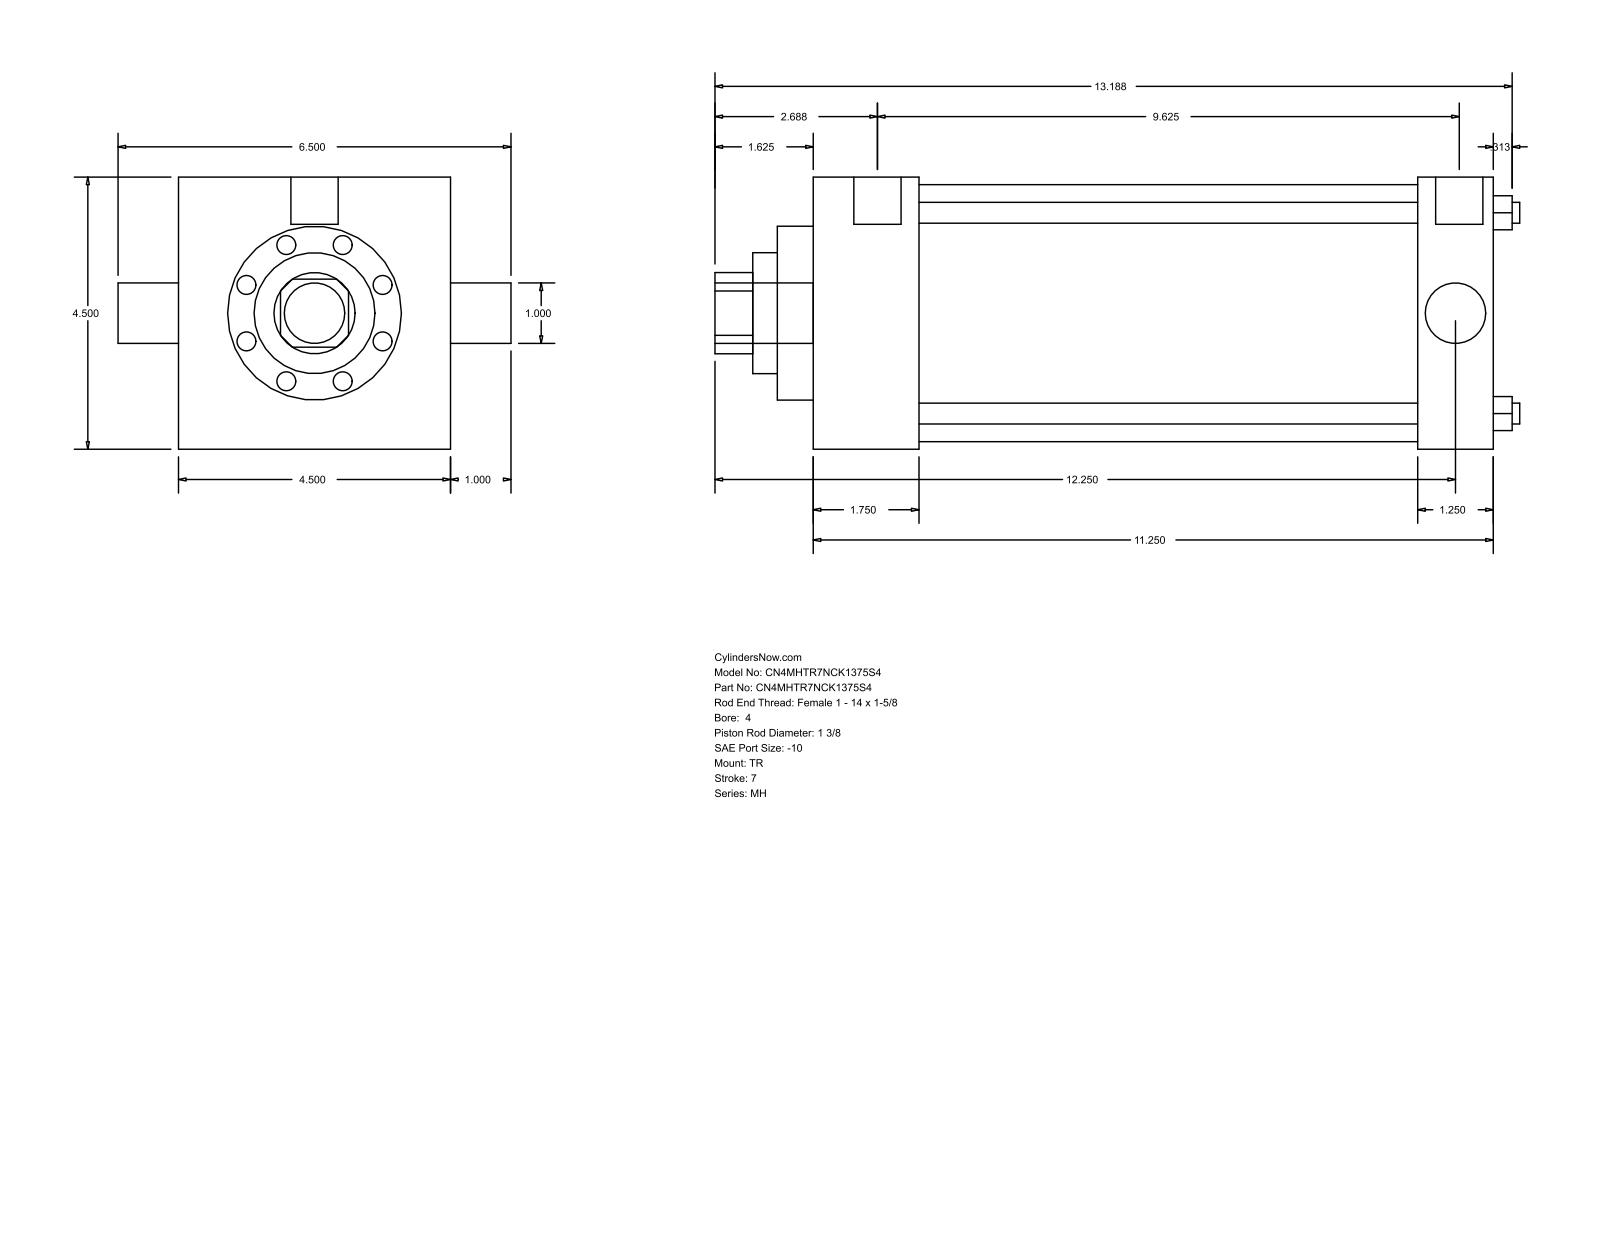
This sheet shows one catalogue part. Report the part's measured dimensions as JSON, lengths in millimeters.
{"part_name": "MH_TR__0400_1.375", "step_written_by": "GSSL Pune (CONFIG_CONTROL_DESIGN)", "units": "millimeters", "bodies": {"solids": 0, "faces": 86, "planar": 61, "cylindrical": 25, "other": 0}, "overall_size": [338.14, 165.1, 114.3], "round_holes": [[8.76, 4], [25.4, 1], [34.92, 1], [50.8, 1], [73.03, 1], [107.95, 1]], "round_bosses_or_shafts": [[8.73, 3], [19.84, 2], [25.4, 1]], "partial_cylinders_radius": [[17.06, 1]], "face_to_face_distances": [114.3, 285.75, 44.45, 241.3, 254, 209.55, 31.75, 15.08, 59.53, 269.08], "hole_center_spacings": [59.62, 84.32, 119.25]}
